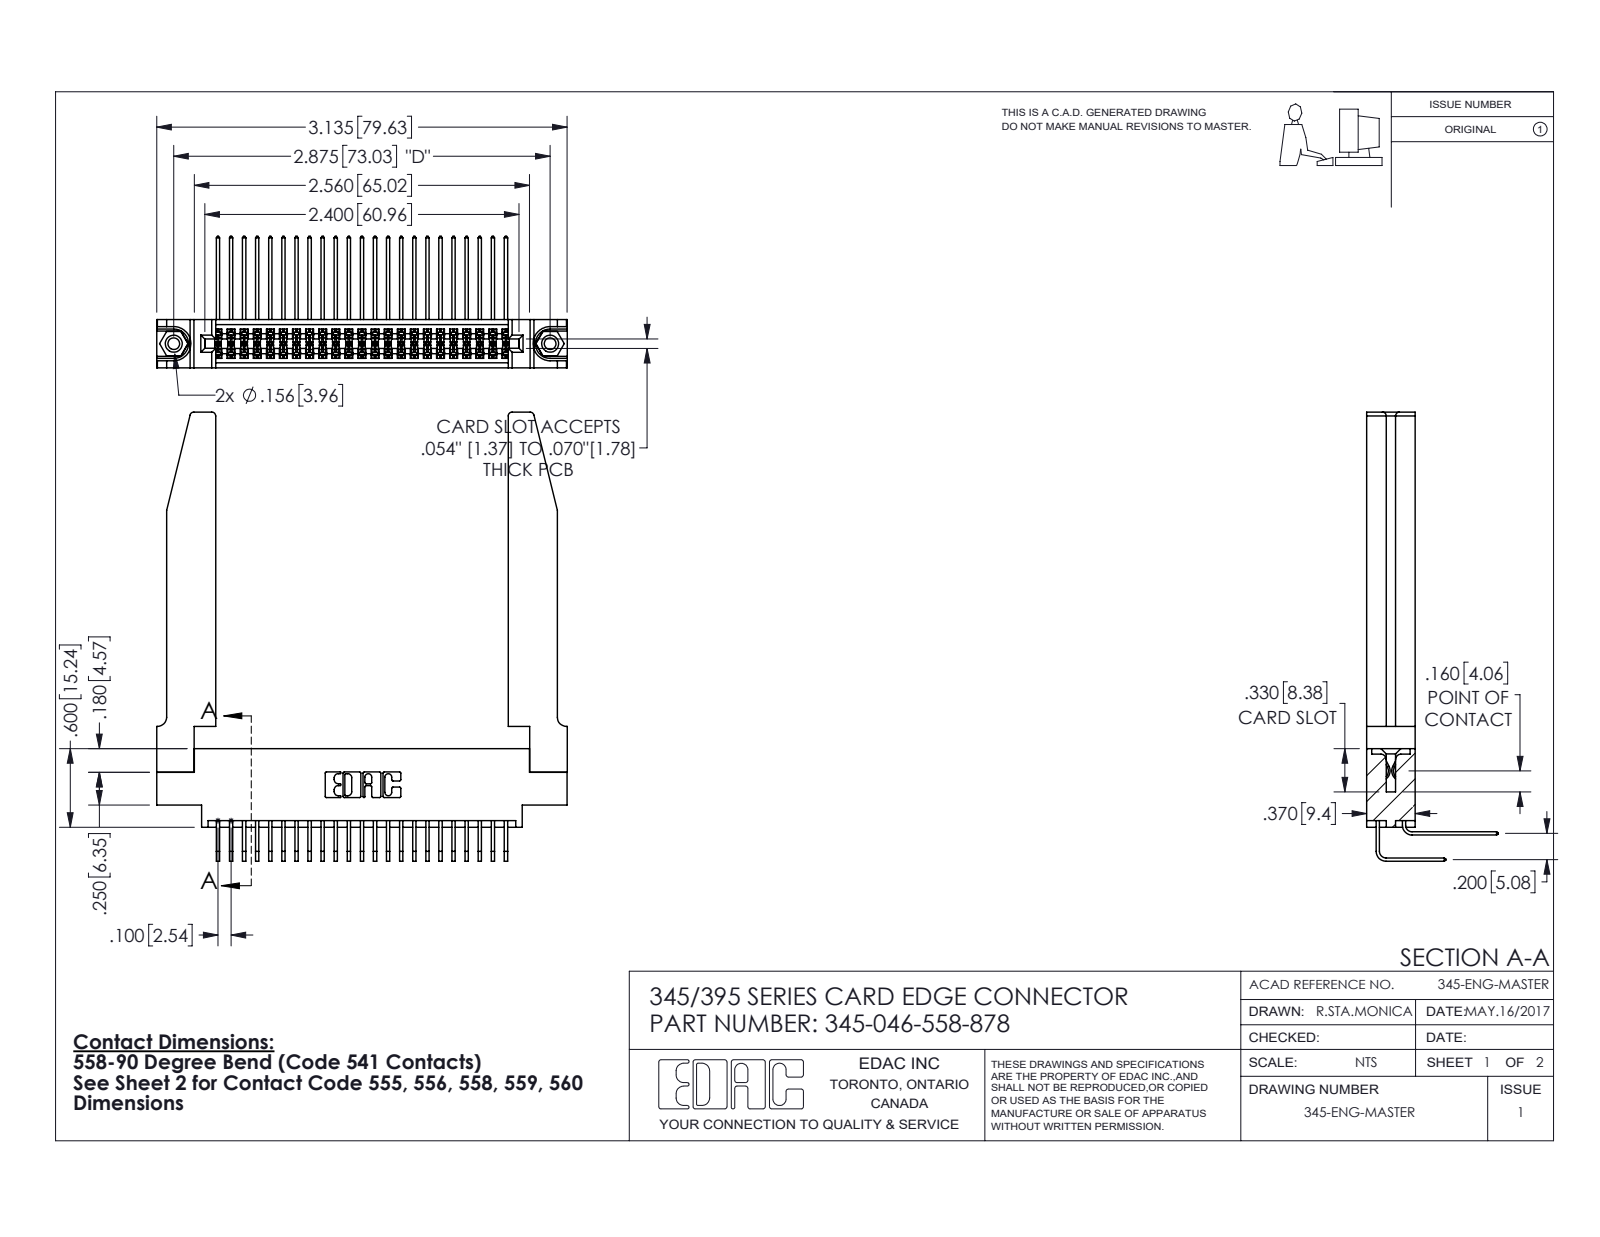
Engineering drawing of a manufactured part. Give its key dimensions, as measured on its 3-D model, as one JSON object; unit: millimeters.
{"part_name": "345-292-001_558 559 Tail - 1; 345-250-001_345-250-001-102; 345-046-558-878; 345-220-078_345-220-078 (+2 more)", "step_written_by": "SolidWorks 2016 (CONFIG_CONTROL_DESIGN)", "units": "millimeters", "bodies": {"solids": 51, "faces": 2756, "planar": 1836, "cylindrical": 868, "other": 52}, "overall_size": [87.1, 79.7, 25.5], "volume_mm3": 15500, "surface_area_mm2": 19260, "round_holes": [[2.3, 2], [3.2, 2], [4, 2], [1.6, 1]], "round_bosses_or_shafts": [[3.9, 2]], "partial_cylinders_radius": [[0.2, 92], [0.3, 22], [0.8, 8], [0.2, 6], [0.8, 6], [0.7, 3], [0.4, 2], [0.5, 2]], "face_to_face_distances": [9.4, 1.8, 7.6, 5.1, 2.5, 6.9, 0.6, 5.7, 3.8, 3.8], "hole_center_spacings": [6.9, 67.1, 73]}
